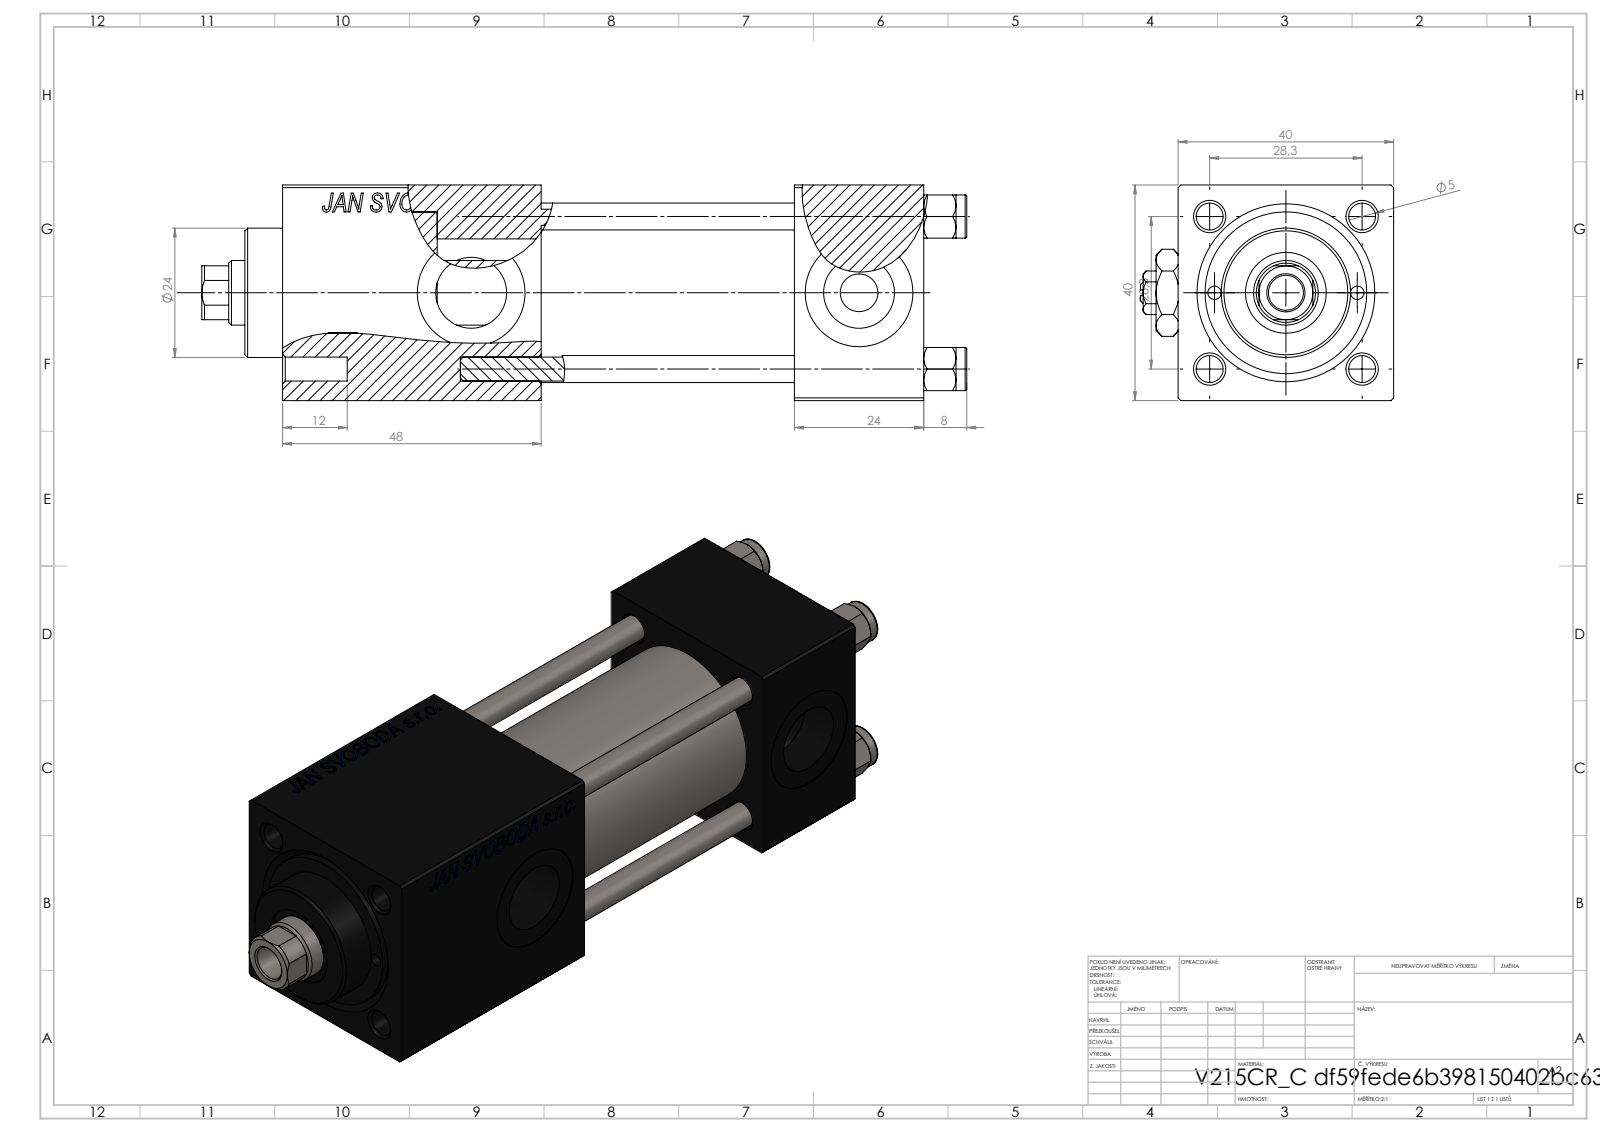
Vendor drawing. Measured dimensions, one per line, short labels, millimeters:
name: V215CR_C_TYCINKA; Zatka_pro_OIL_PORT; NUT_M5_C; V215_VC_A (+2 more)
written by: SolidWorks 2019 (CONFIG_CONTROL_DESIGN)
unit: mm
bodies: 13 solids, 1254 faces (574 planar, 102 cylindrical, 578 other)
size: 142 × 47 × 40
volume: 140 936 mm³; area: 56 288 mm²
holes: 4× ⌀5, 3× ⌀20, 2× ⌀2.5, 2× ⌀7, 2× ⌀13.16, 1× ⌀6.5, 1× ⌀12, 1× ⌀15, 1× ⌀25, 1× ⌀30
bosses: 4× ⌀8, 1× ⌀31, 1× ⌀24
rounds: 1× R5.5
face distances: 40, 24, 39.8, 90.3, 66.3, 47, 48, 71, 19.3, 95
hole spacings: 14.18, 20.01, 28.3, 30.84, 13.25, 40.02, 26.5, 72
